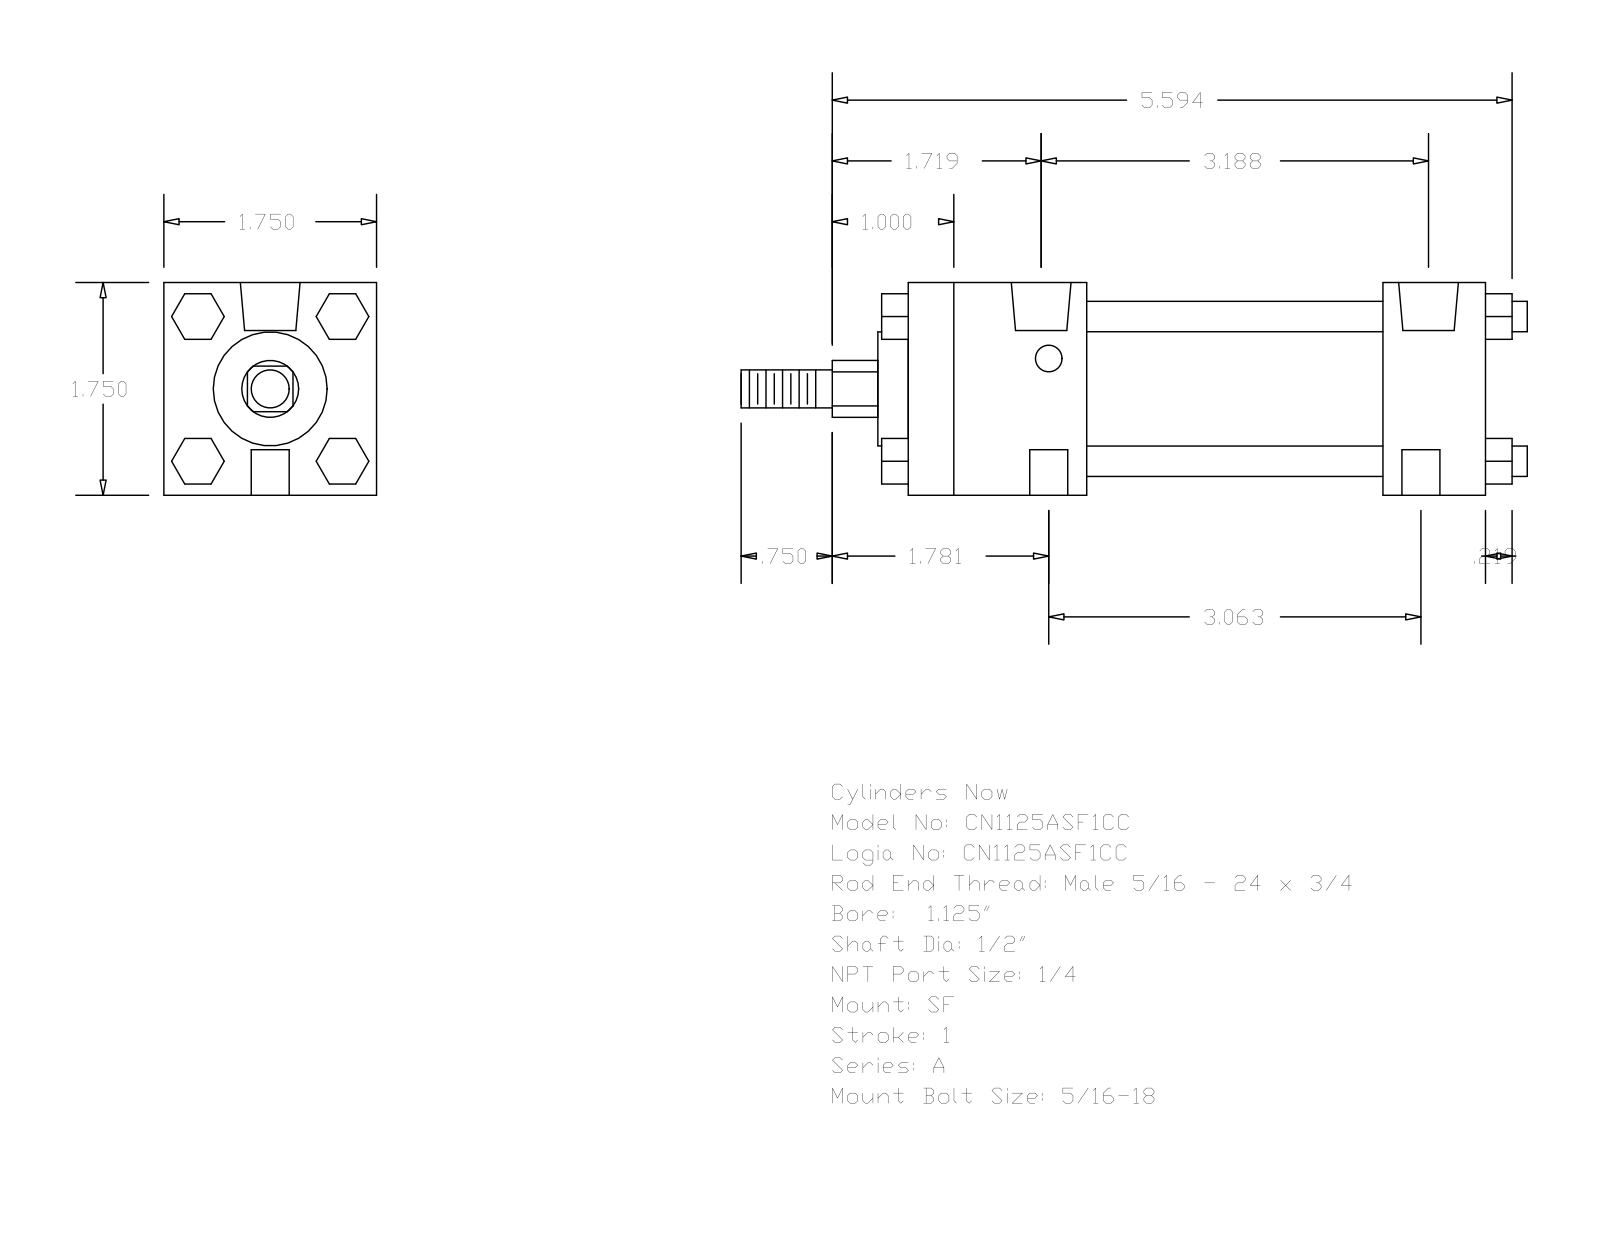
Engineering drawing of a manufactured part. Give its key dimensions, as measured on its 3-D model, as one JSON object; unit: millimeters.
{"part_name": "A_SF__0112_0.5", "step_written_by": "GSSL Pune (CONFIG_CONTROL_DESIGN)", "units": "millimeters", "bodies": {"solids": 0, "faces": 120, "planar": 92, "cylindrical": 28, "other": 0}, "overall_size": [164.31, 44.45, 44.45], "round_holes": [[5.56, 2], [7.94, 2], [12.49, 2]], "round_bosses_or_shafts": [[6.35, 4], [31.88, 1], [23.81, 1], [12.7, 1], [7.94, 1]], "partial_cylinders_radius": [[5.94, 1]], "face_to_face_distances": [44.46, 120.65, 99.21, 21.44, 37.3, 61.91, 83.35, 9.53, 5.59, 26.99], "hole_center_spacings": [77.79, 1.58, 1.59, 79.37, 79.38, 80.96]}
